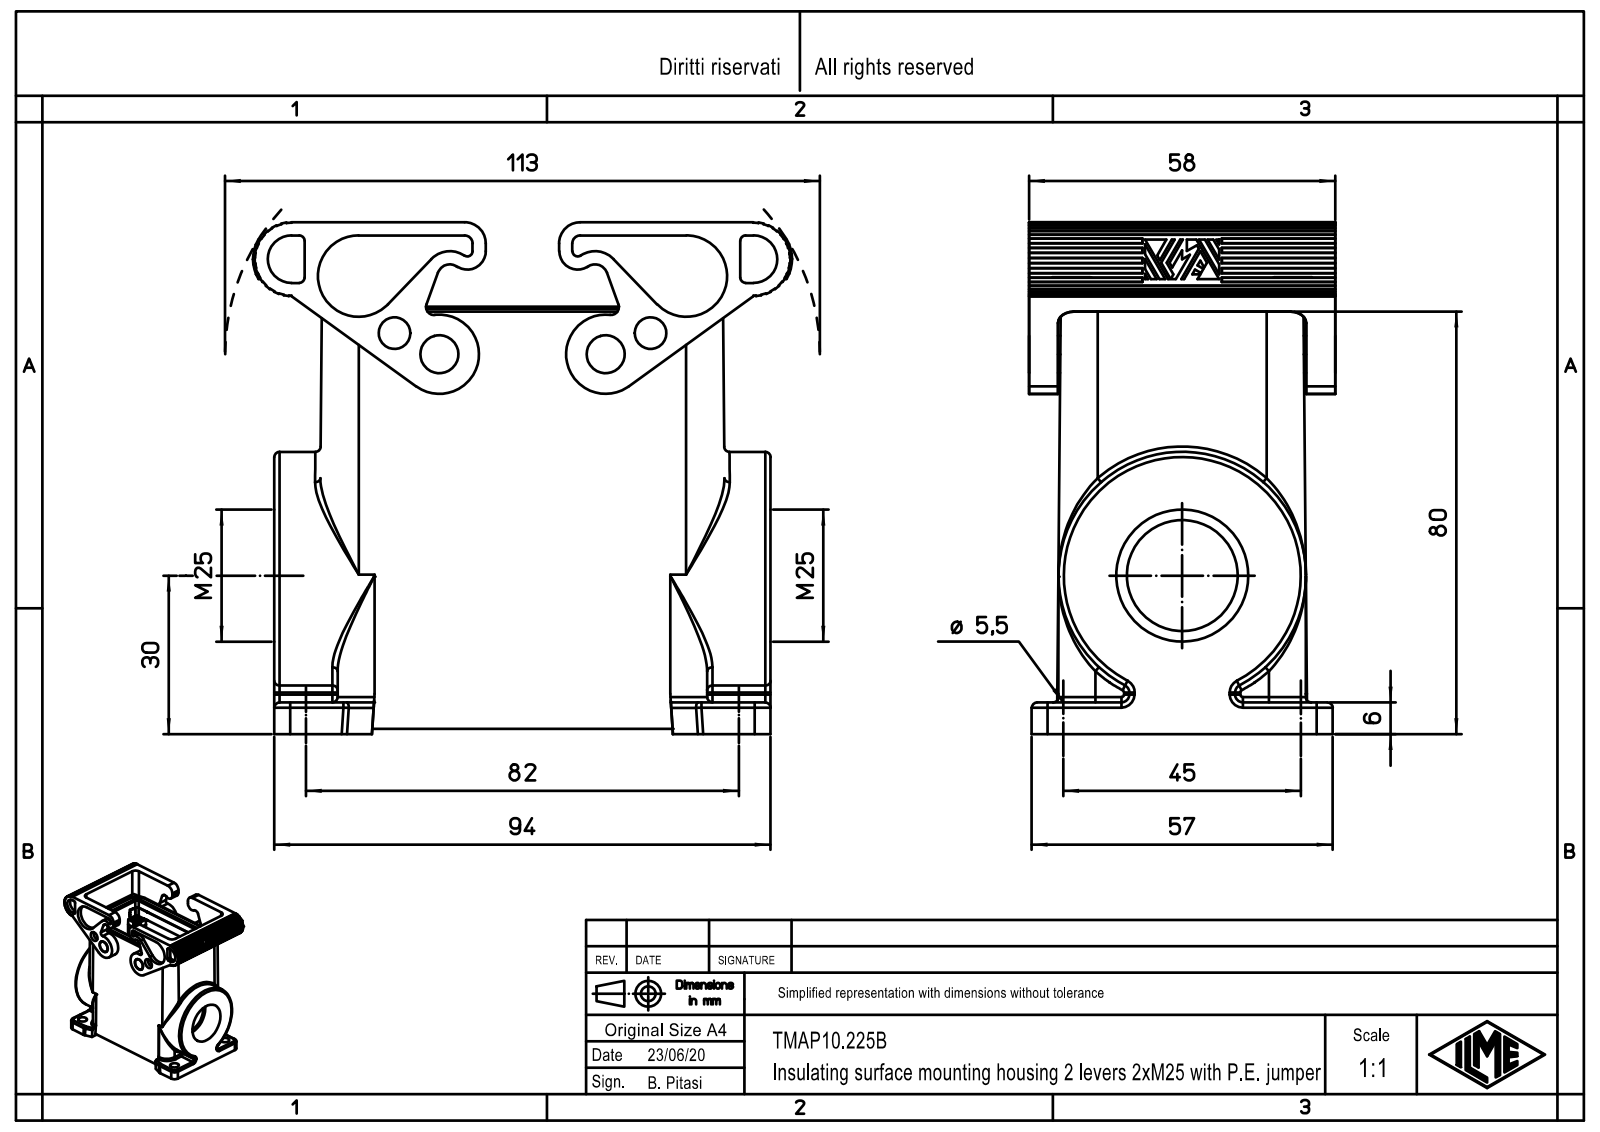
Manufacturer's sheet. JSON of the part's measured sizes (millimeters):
{"part_name": "TMAP10.225B", "step_written_by": "Creo Elements/Direct Modeling 20.1B 02-Apr-2019 (C) Parametric Technology GmbH (AUTOMOTIVE_DESIGN)", "units": "millimeters", "bodies": {"solids": 1, "faces": 944, "planar": 536, "cylindrical": 276, "other": 132}, "overall_size": [102.1, 96.9, 58], "volume_mm3": 189420, "surface_area_mm2": 65522, "round_holes": [[3, 4], [3.5, 4], [5.5, 4], [6, 2], [10, 2], [21, 1], [25, 1]], "round_bosses_or_shafts": [[4.8, 4], [7, 2], [46.87, 1]], "partial_cylinders_radius": [[1, 20], [1.5, 20], [3, 12], [3.5, 6], [7, 6], [0.5, 4], [1.3, 4], [1.6, 4]], "face_to_face_distances": [40.6, 5.5, 52.5, 1, 62.6, 2.5, 55.5, 6.5, 50, 3], "hole_center_spacings": [15.4, 38.11, 70.08, 78.27, 9.39, 27, 40.2, 45]}
